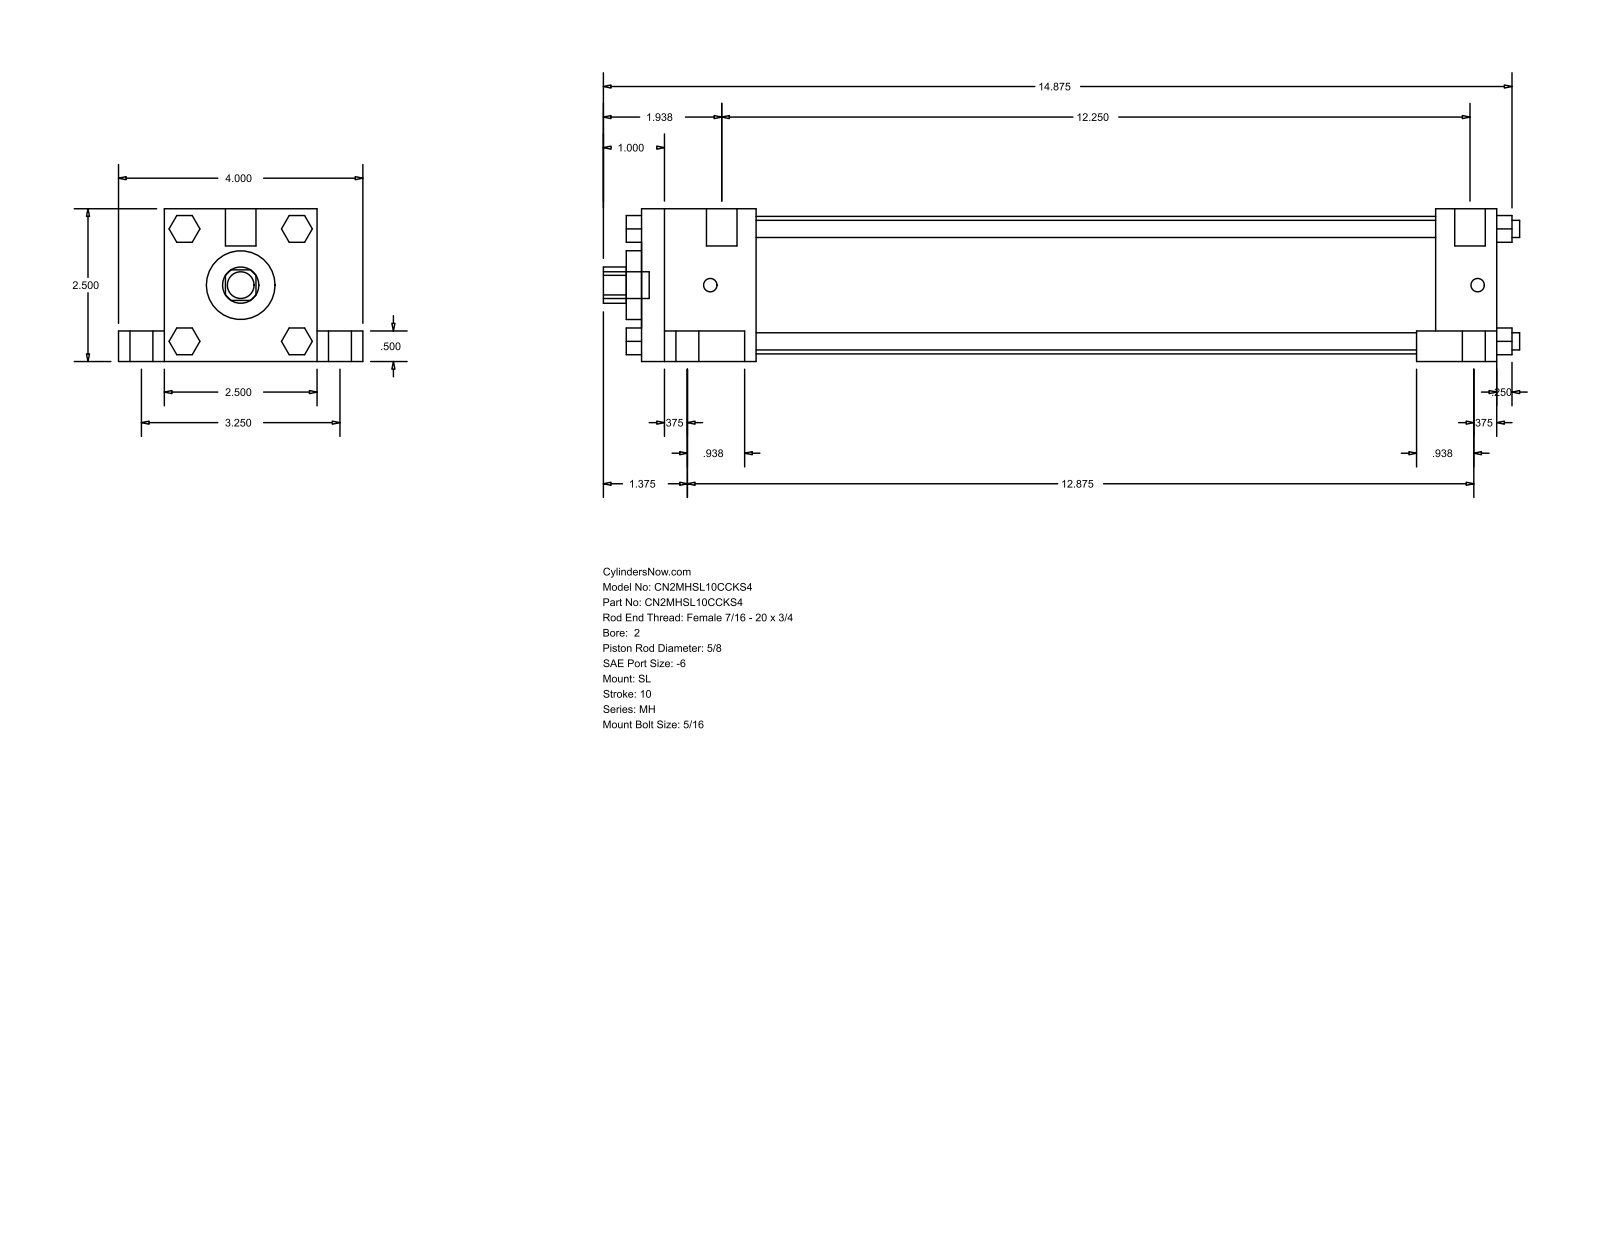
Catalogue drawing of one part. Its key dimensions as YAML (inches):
part_name: "MH_SL__0200_0.625"
step_written_by: "GSSL Pune (CONFIG_CONTROL_DESIGN)"
units: inches
bodies: {solids: 0, faces: 148, planar: 112, cylindrical: 36, other: 0}
overall_size: [15, 4, 2.5]
round_holes:
  - {diameter: 0.625, count: 1}
  - {diameter: 1.125, count: 1}
  - {diameter: 2.25, count: 1}
round_bosses_or_shafts:
  - {diameter: 0.625, count: 4}
  - {diameter: 0.375, count: 4}
  - {diameter: 0.281, count: 4}
  - {diameter: 0.219, count: 4}
  - {diameter: 0.5, count: 2}
  - {diameter: 0.437, count: 1}
partial_cylinders:
  - {radius: 0.297, count: 1}
face_to_face_distances: [2.5, 14, 0.5, 0.75, 2, 3.25, 13, 1, 1.875, 11.125]
